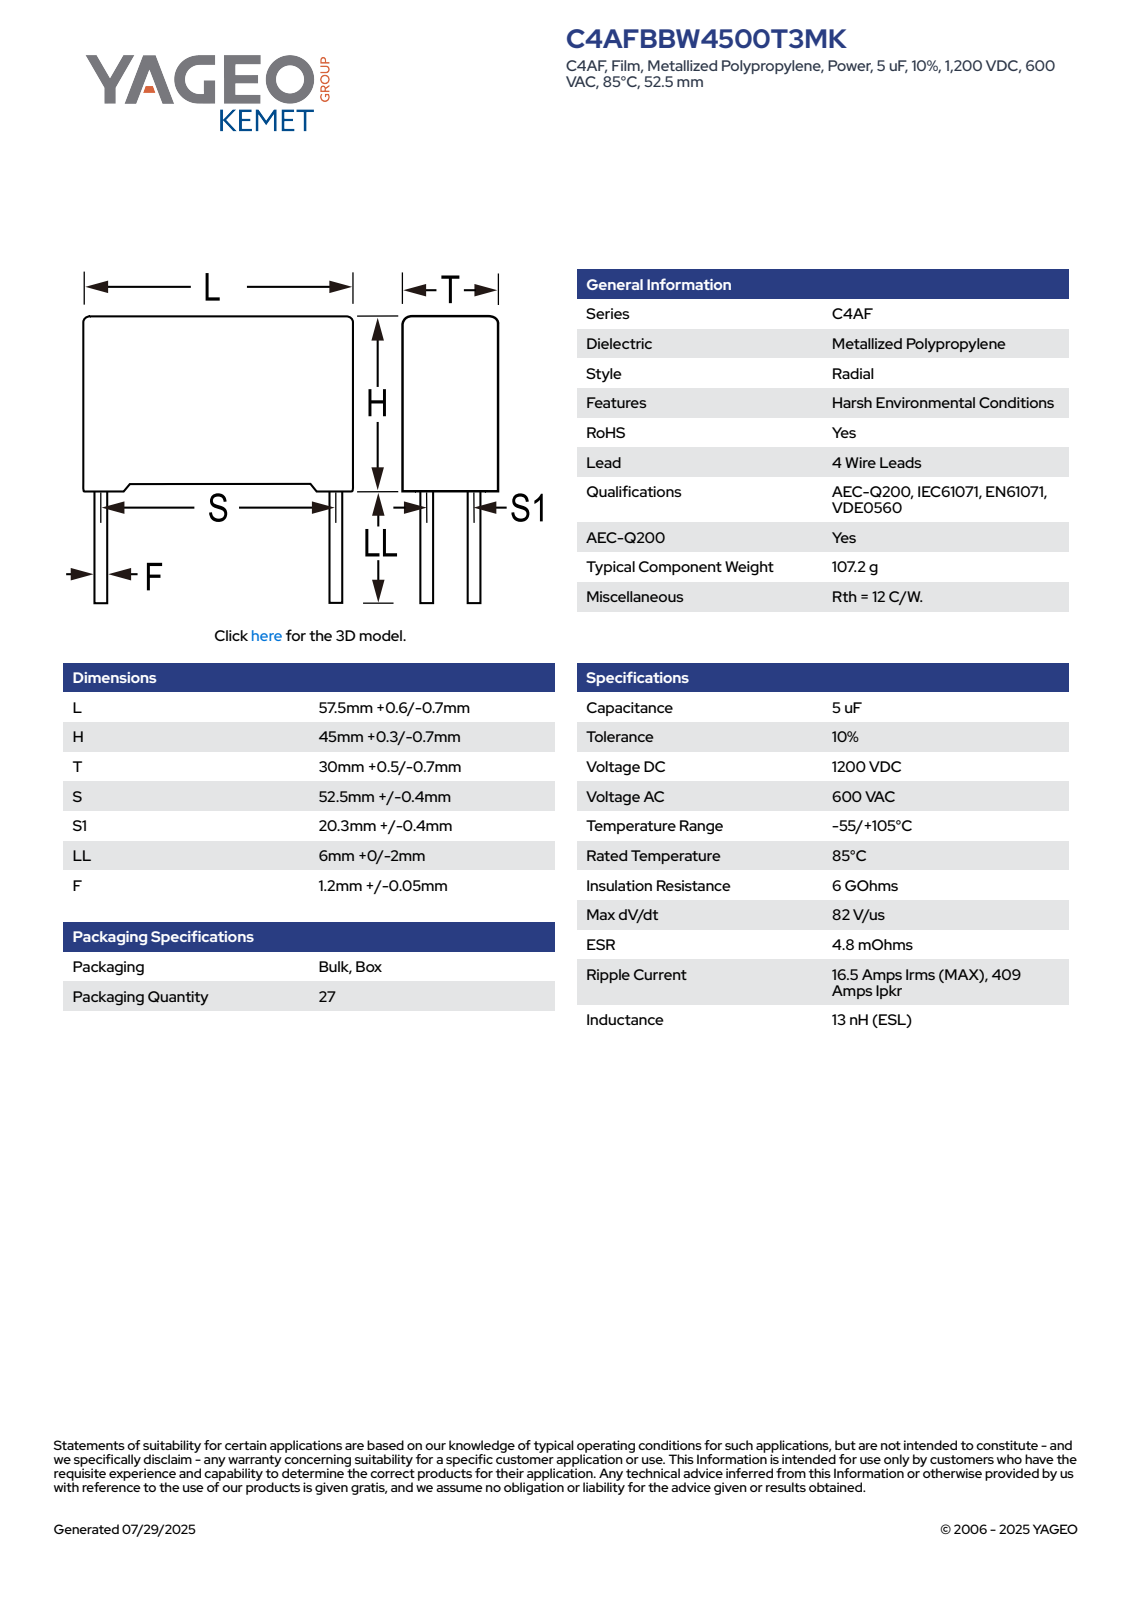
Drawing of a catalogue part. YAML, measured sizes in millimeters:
part_name: "CFP_RB4_57.5X45X3_L58.1H45.3T30.5S52.5S120.3LL6F1.25"
step_written_by: "SolidWorks 2014 (AUTOMOTIVE_DESIGN)"
units: millimeters
bodies: {solids: 4, faces: 87, planar: 79, cylindrical: 8, other: 0}
overall_size: [58.1, 51.3, 30.5]
volume: 78160
surface_area: 11898
round_bosses_or_shafts:
  - {diameter: 1.25, count: 4}
face_to_face_distances: [30.5, 43.97, 58.1, 1.33, 45.3, 30.51, 1.87, 56.23, 54.36, 28.63]
